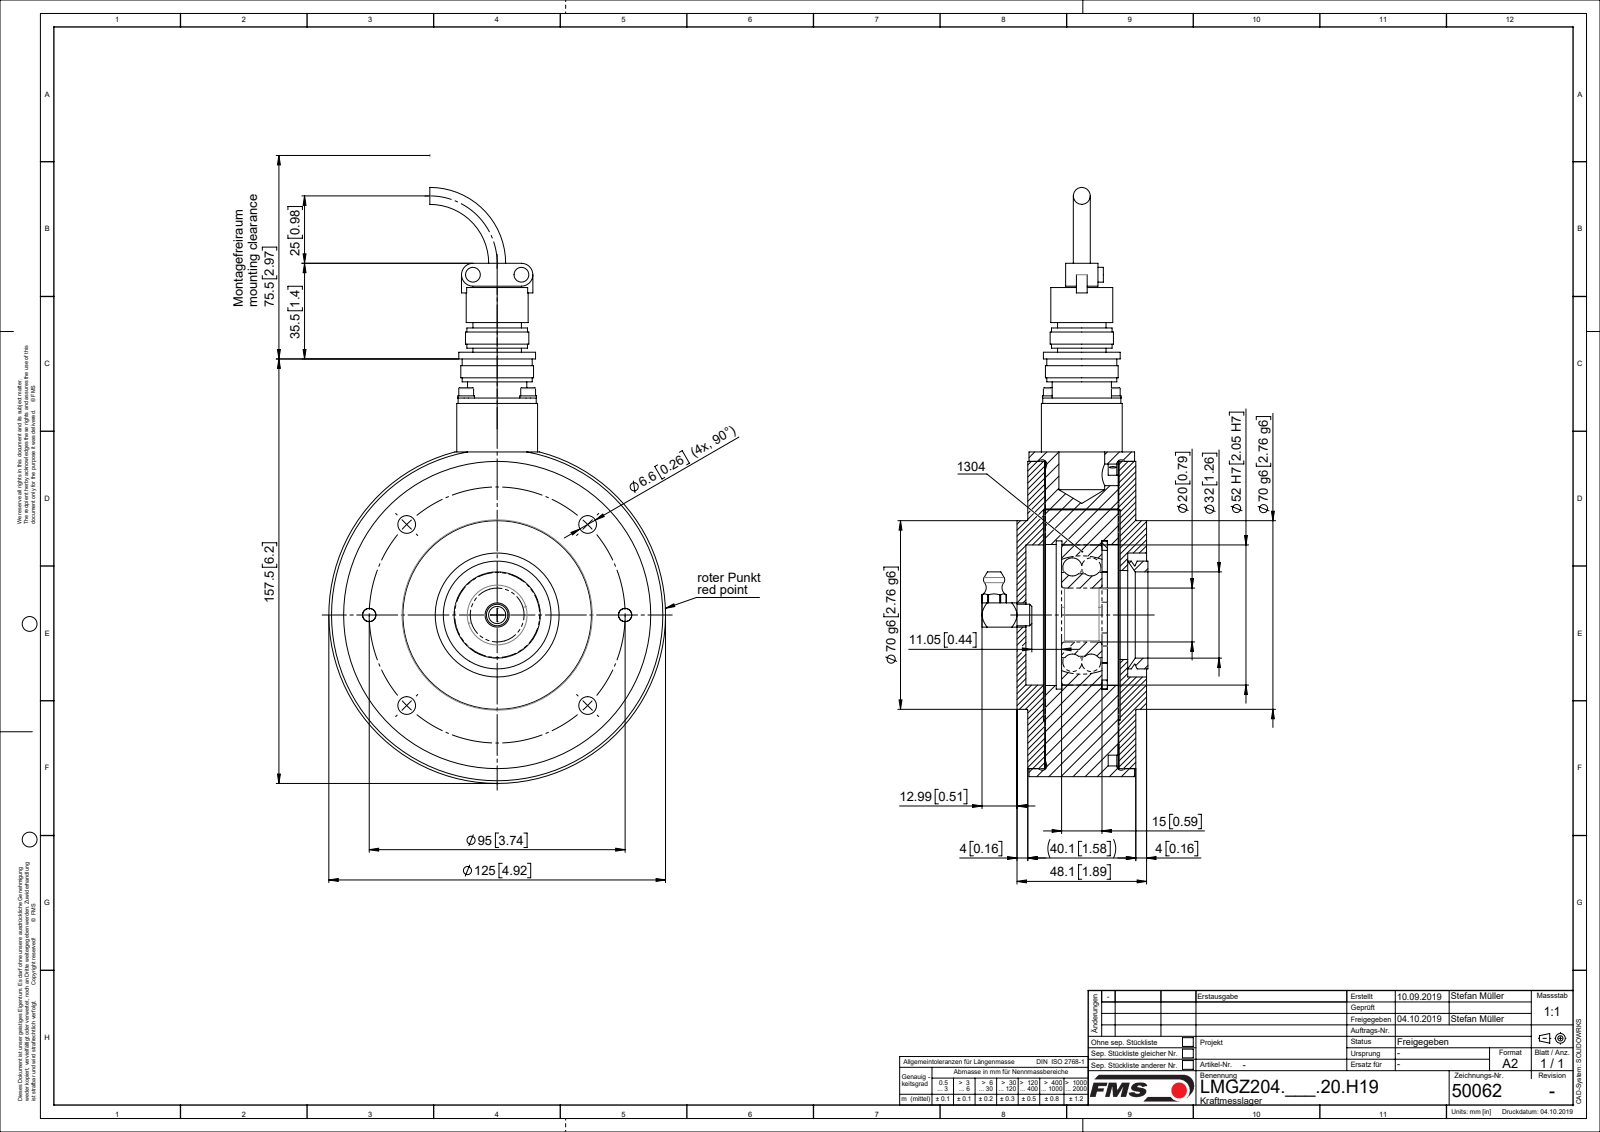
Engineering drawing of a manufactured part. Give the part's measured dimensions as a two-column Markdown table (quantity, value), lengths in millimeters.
| quantity | value |
| --- | --- |
| part name | ZEICHNUNG7; L50062; L4832404; L47955 (+8 more) |
| STEP written by | Mechanical Desktop 2007 (CONFIG_CONTROL_DESIGN) |
| units | millimeters |
| bodies | 21 solids, 432 faces (120 planar, 250 cylindrical, 62 other) |
| overall size | 221.15 × 125 × 62.6 |
| volume | 485 632 mm³ |
| surface area | 145 716 mm² |
| round holes (diameter × count) | 6.6 × 6, 2.6 × 4, 3.2 × 4, 3.4 × 4, 5 × 2, 11 × 2, 8.68 × 1, 20 × 1, 23 × 1, 31 × 1, 33 × 1, 37.9 × 1 |
| round bosses / shafts (diameter × count) | 5.5 × 6, 6.2 × 4, 3 × 4, 2.5 × 4, 10 × 3, 6 × 2, 125 × 1, 114 × 1 |
| partial cylindrical surfaces (radius × count) | 5 × 8, 4.25 × 2, 40.5 × 1, 47 × 1 |
| main face-to-face distances | 27.25, 33.55, 6.3, 6.55, 33.8, 27, 27.5, 4, 10.55, 37.8 |
| hole center spacings | 47.5, 16.26, 23, 36.36, 67.18, 87.77, 32.53, 95.01 |
